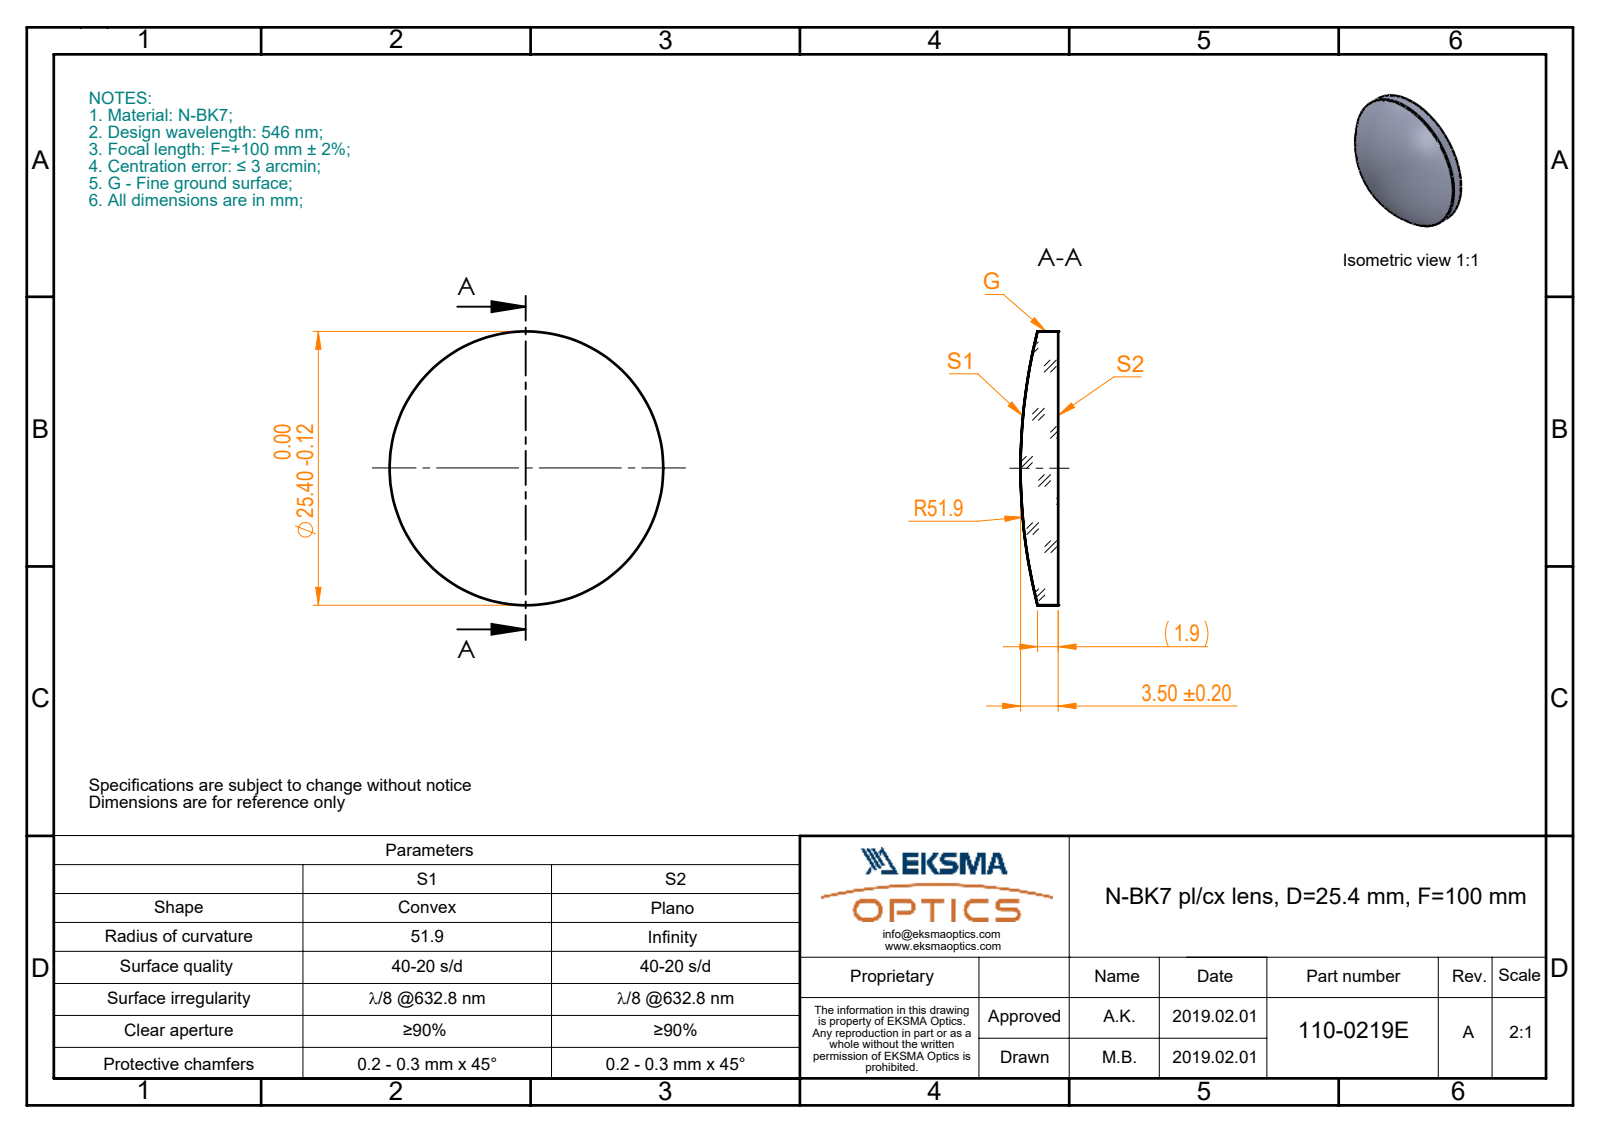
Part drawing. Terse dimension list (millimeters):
name: 110-0219E BK7 pl-cx 25.4 F100
written by: SolidWorks 2017 (CONFIG_CONTROL_DESIGN)
unit: mm
bodies: 1 solid, 5 faces (1 planar, 2 cylindrical, 2 other)
size: 25.4 × 25.4 × 3.5
volume: 1 376 mm³; area: 1 175 mm²
bosses: 1× ⌀25.4
